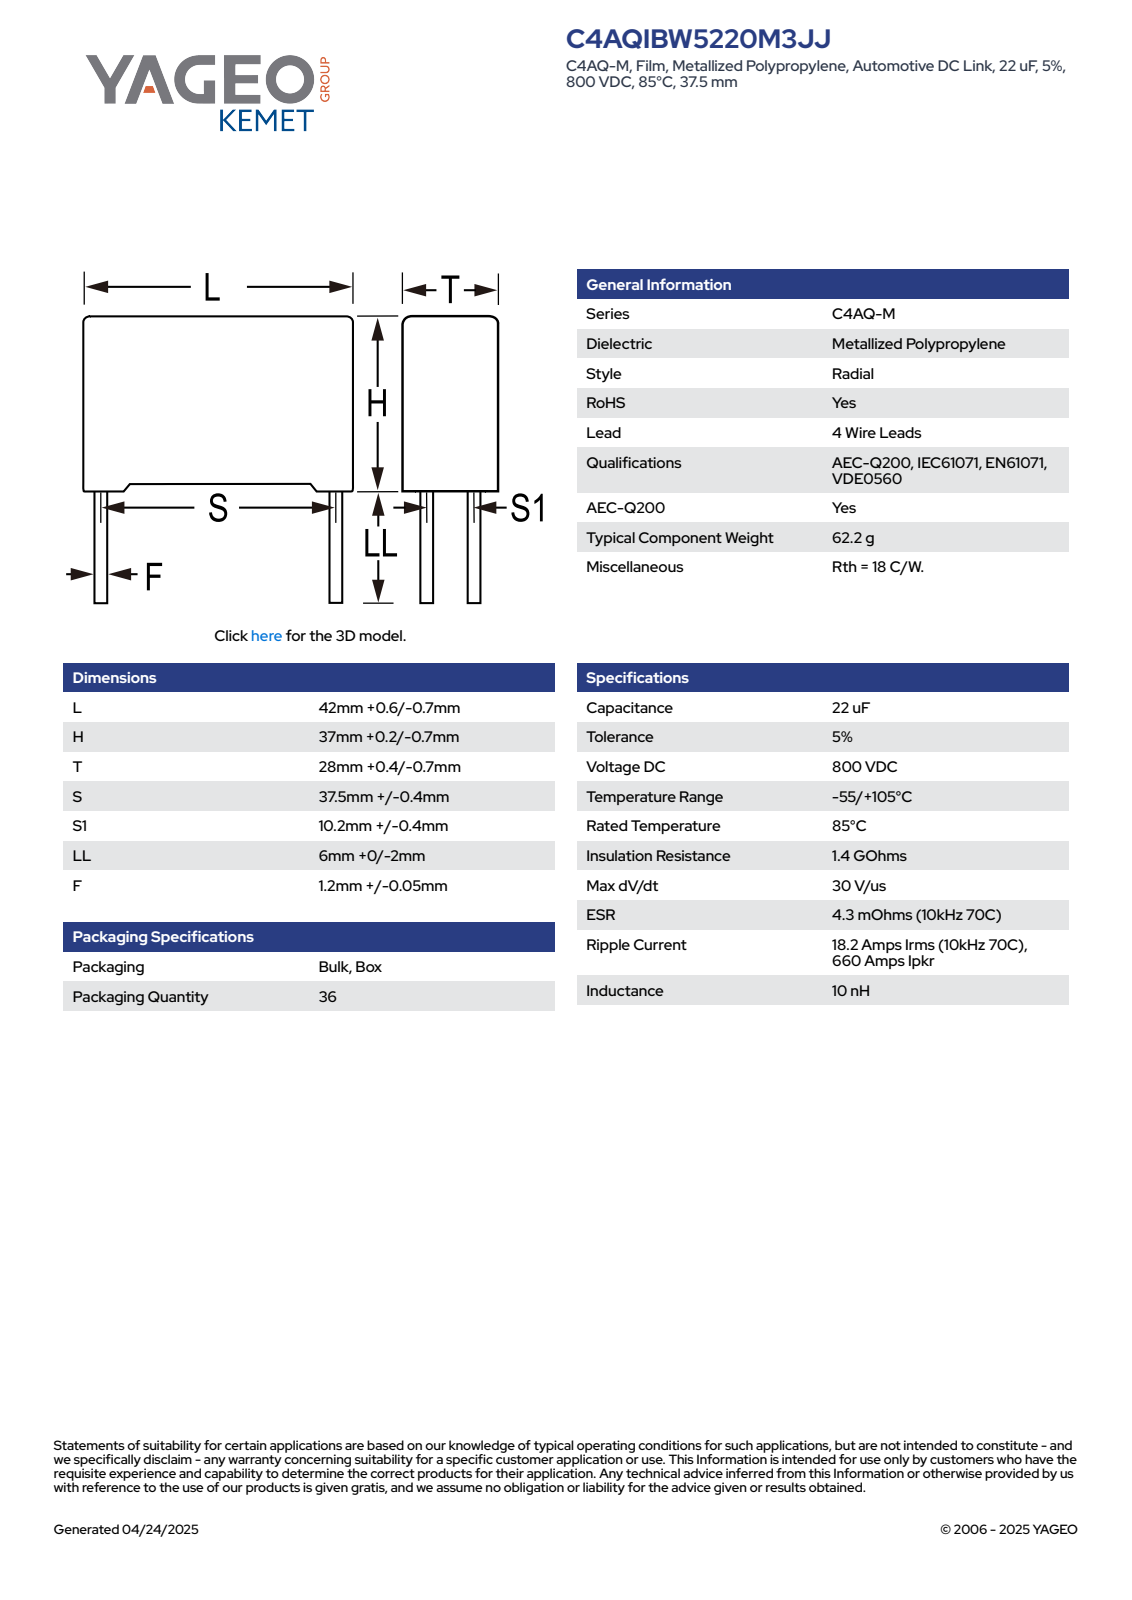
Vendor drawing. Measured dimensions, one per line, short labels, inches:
name: CFP_RB4_42X37X28_L42.6H37.2T28.4S37.5S110.2LL6F1.25
written by: SolidWorks 2014 (AUTOMOTIVE_DESIGN)
unit: in
bodies: 4 solids, 87 faces (79 planar, 8 cylindrical, 0 other)
size: 1.701 × 1.677 × 1.119
volume: 2.677 in³; area: 12.33 in²
bosses: 4× ⌀0.049
face distances: 1.118, 1.422, 1.677, 0.043, 1.465, 0.069, 1.119, 1.608, 1.539, 1.049
